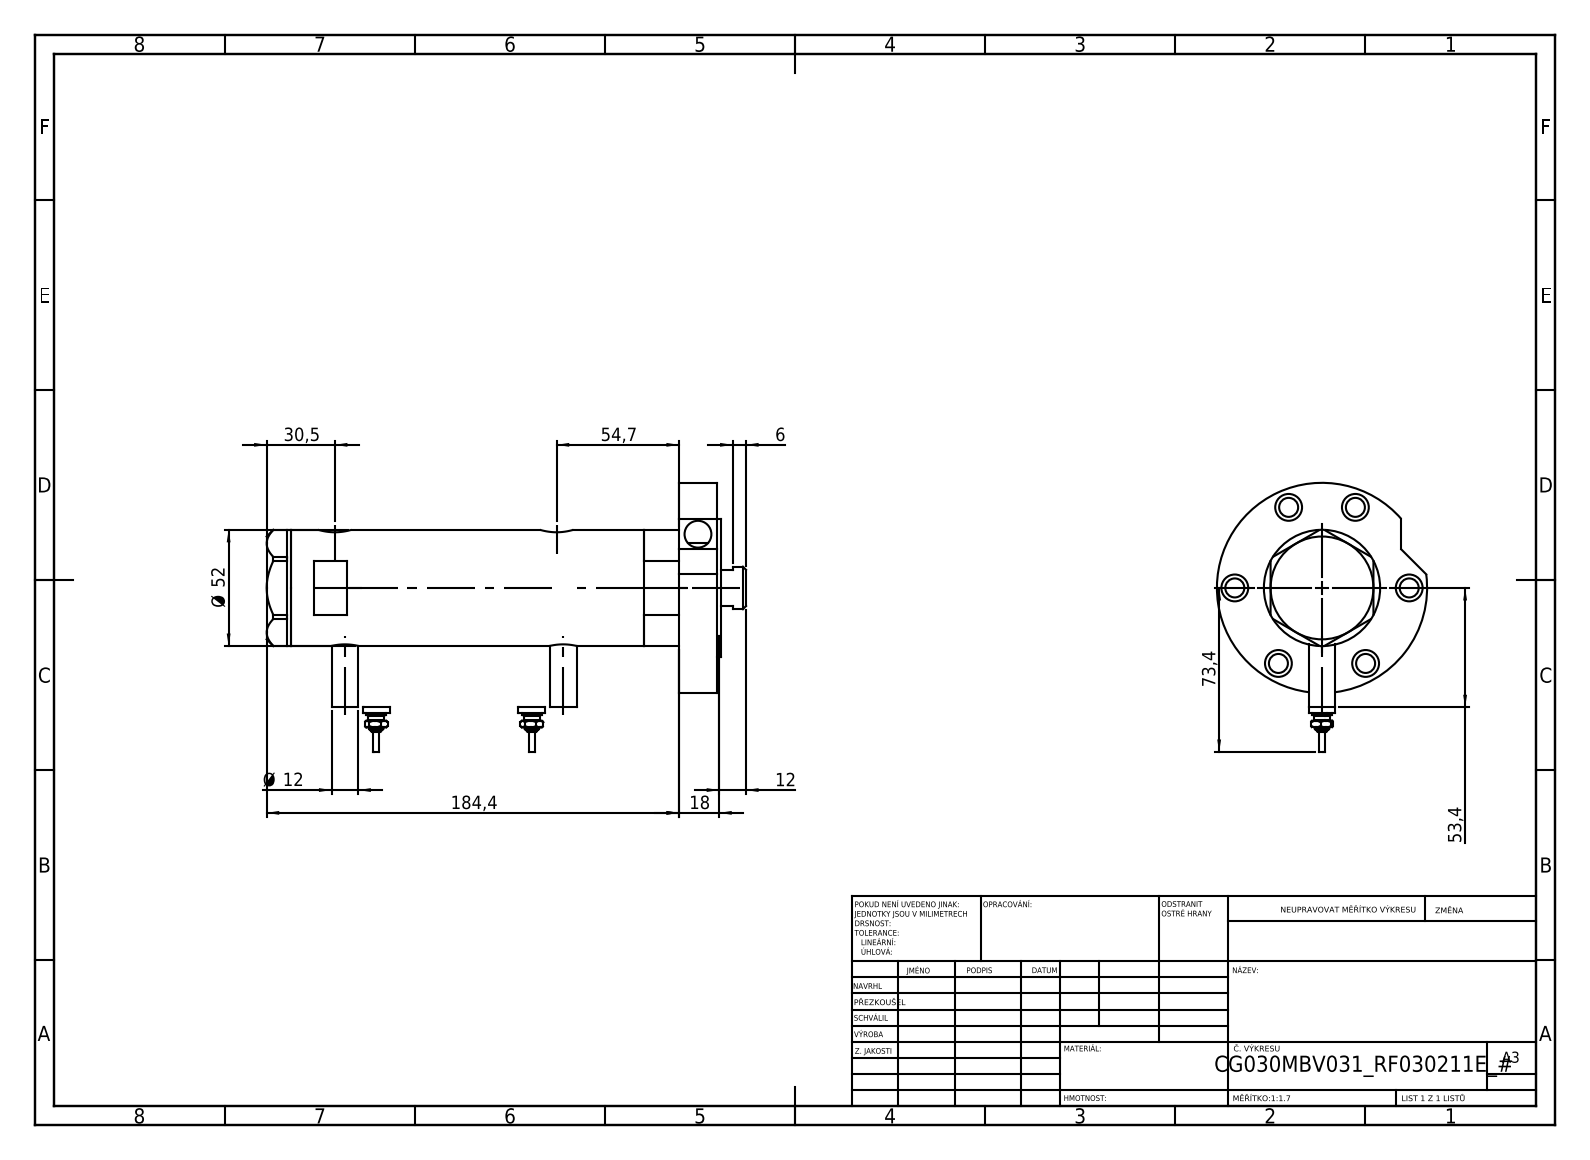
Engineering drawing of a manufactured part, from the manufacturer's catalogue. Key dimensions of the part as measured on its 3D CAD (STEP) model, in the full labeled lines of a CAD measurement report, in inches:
Part name (STEP PRODUCT): V270CG_VC; V270CG_MIDDLE; Switch; V270CG_FRONT (+2 more)
STEP written by: SolidWorks 2019 (CONFIG_CONTROL_DESIGN)
Units: inches
Bodies: 7 solids, 270 faces (104 planar, 102 cylindrical, 64 other)
Overall size (bounding box): 8.441 × 4.74 × 3.701
Volume: 29.66 in³ · Surface area: 177 in²
Round holes (diameter × count): ⌀0.472 ×7, ⌀0.335 ×6, ⌀0.383 ×2, ⌀0.492 ×2, ⌀0.591 ×2, ⌀0.256 ×1, ⌀0.787 ×1, ⌀0.846 ×1, ⌀1.181 ×1, ⌀1.299 ×1, ⌀1.575 ×1, ⌀1.732 ×1
Round bosses / shafts (diameter × count): ⌀0.472 ×4, ⌀0.354 ×2, ⌀0.276 ×2, ⌀0.177 ×2, ⌀0.098 ×2, ⌀3.701 ×1, ⌀2.441 ×1, ⌀2.047 ×1
Main face-to-face distances: 0.669, 6.827, 7.496, 0.079, 7.575, 4.783, 2.043, 2.713, 0.433, 8.008
Hole centre spacings: 1.535, 1.706, 2.553, 2.659, 2.754, 3.064, 0.114, 0.177
